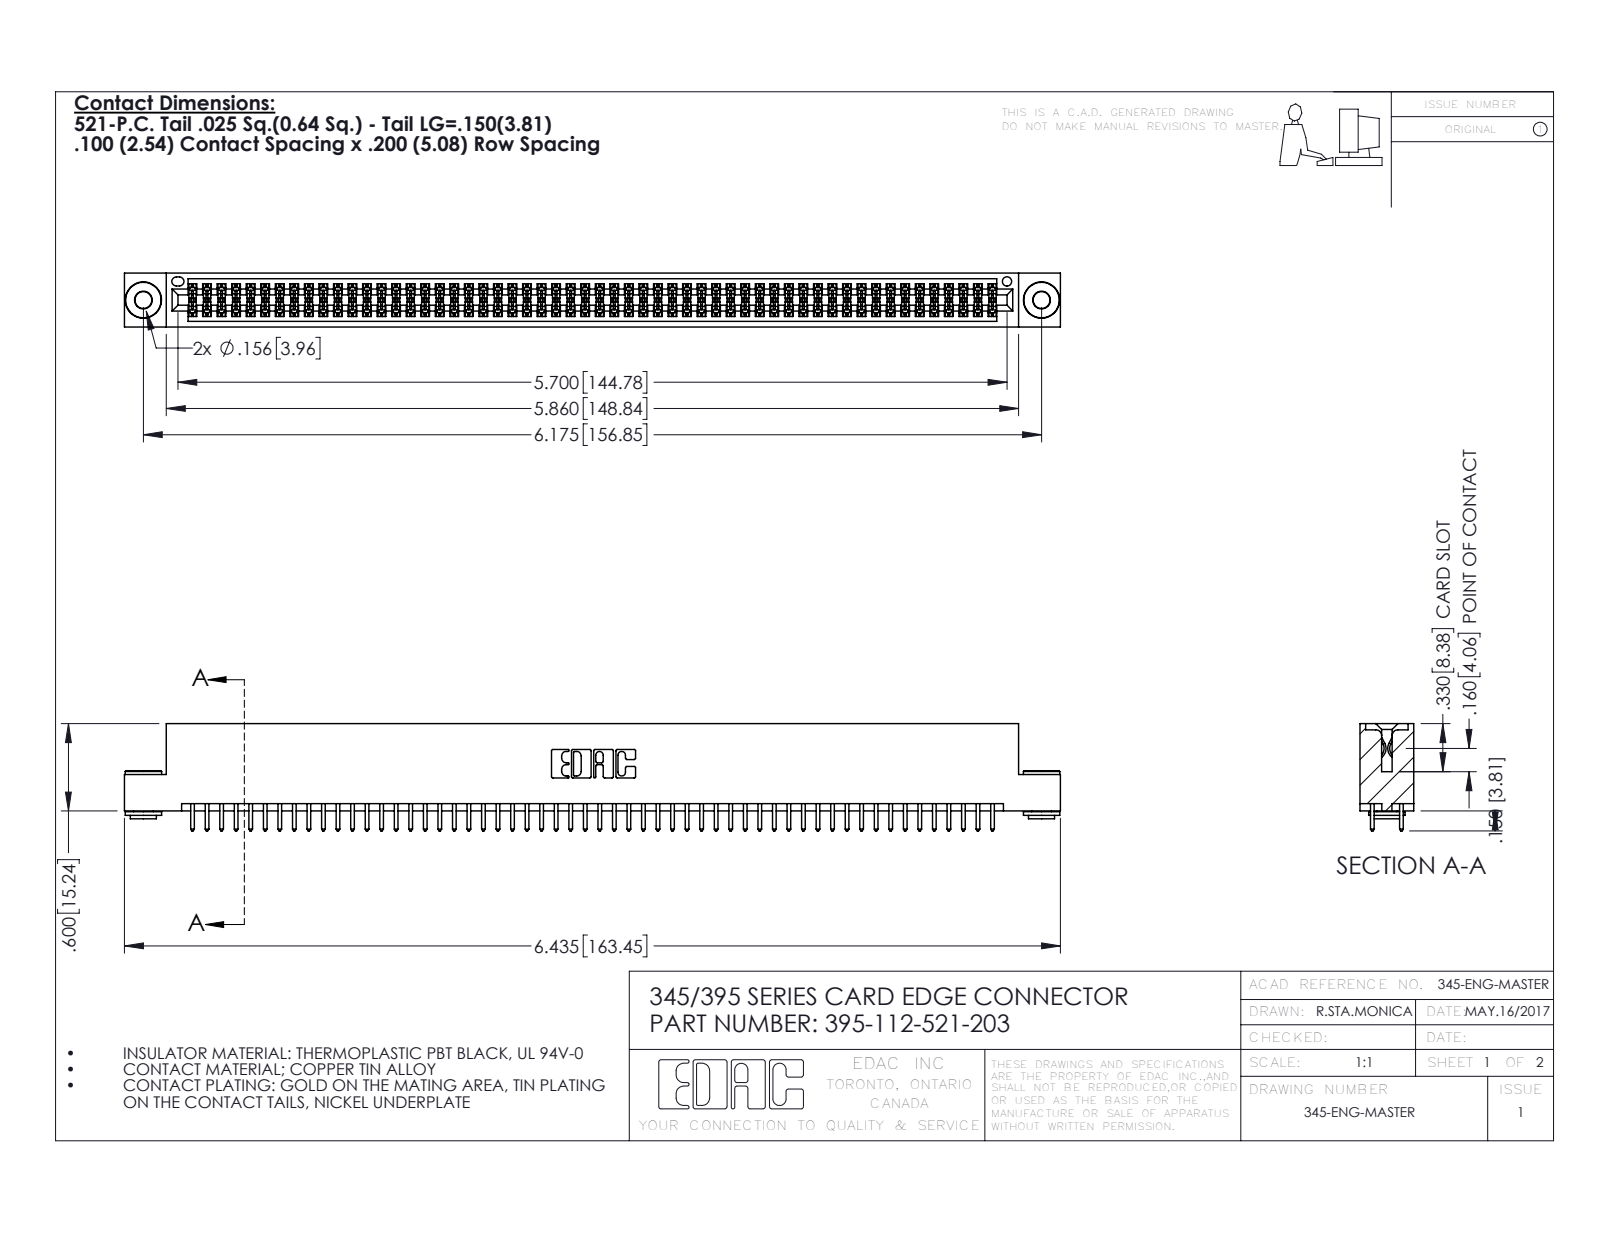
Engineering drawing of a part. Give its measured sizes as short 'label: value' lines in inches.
name: 345-292-001_345-293-121; 345 Part_Flush Mounting Lugs - 0.156 Dia-TH; 345-250-002_345-250-002-102; 395-112-521-203
written by: SolidWorks 2016 (CONFIG_CONTROL_DESIGN)
unit: in
bodies: 115 solids, 5764 faces (3786 planar, 1970 cylindrical, 8 other)
size: 6.435 × 0.737 × 0.37
volume: 0.975 in³; area: 36.89 in²
holes: 2× ⌀0.116, 2× ⌀0.156, 1× ⌀0.064
bosses: 2× ⌀0.25, 2× ⌀0.18, 2× ⌀0.136
rounds: 168× R0.006, 112× R0.01, 22× R0.01, 6× R0.007, 6× R0.031, 3× R0.026, 2× R0.014, 2× R0.019
face distances: 0.072, 0.298, 0.2, 0.025, 0.098, 0.272, 0.37, 0.225, 0.175, 0.149
hole spacings: 0.27, 5.939, 6.175
